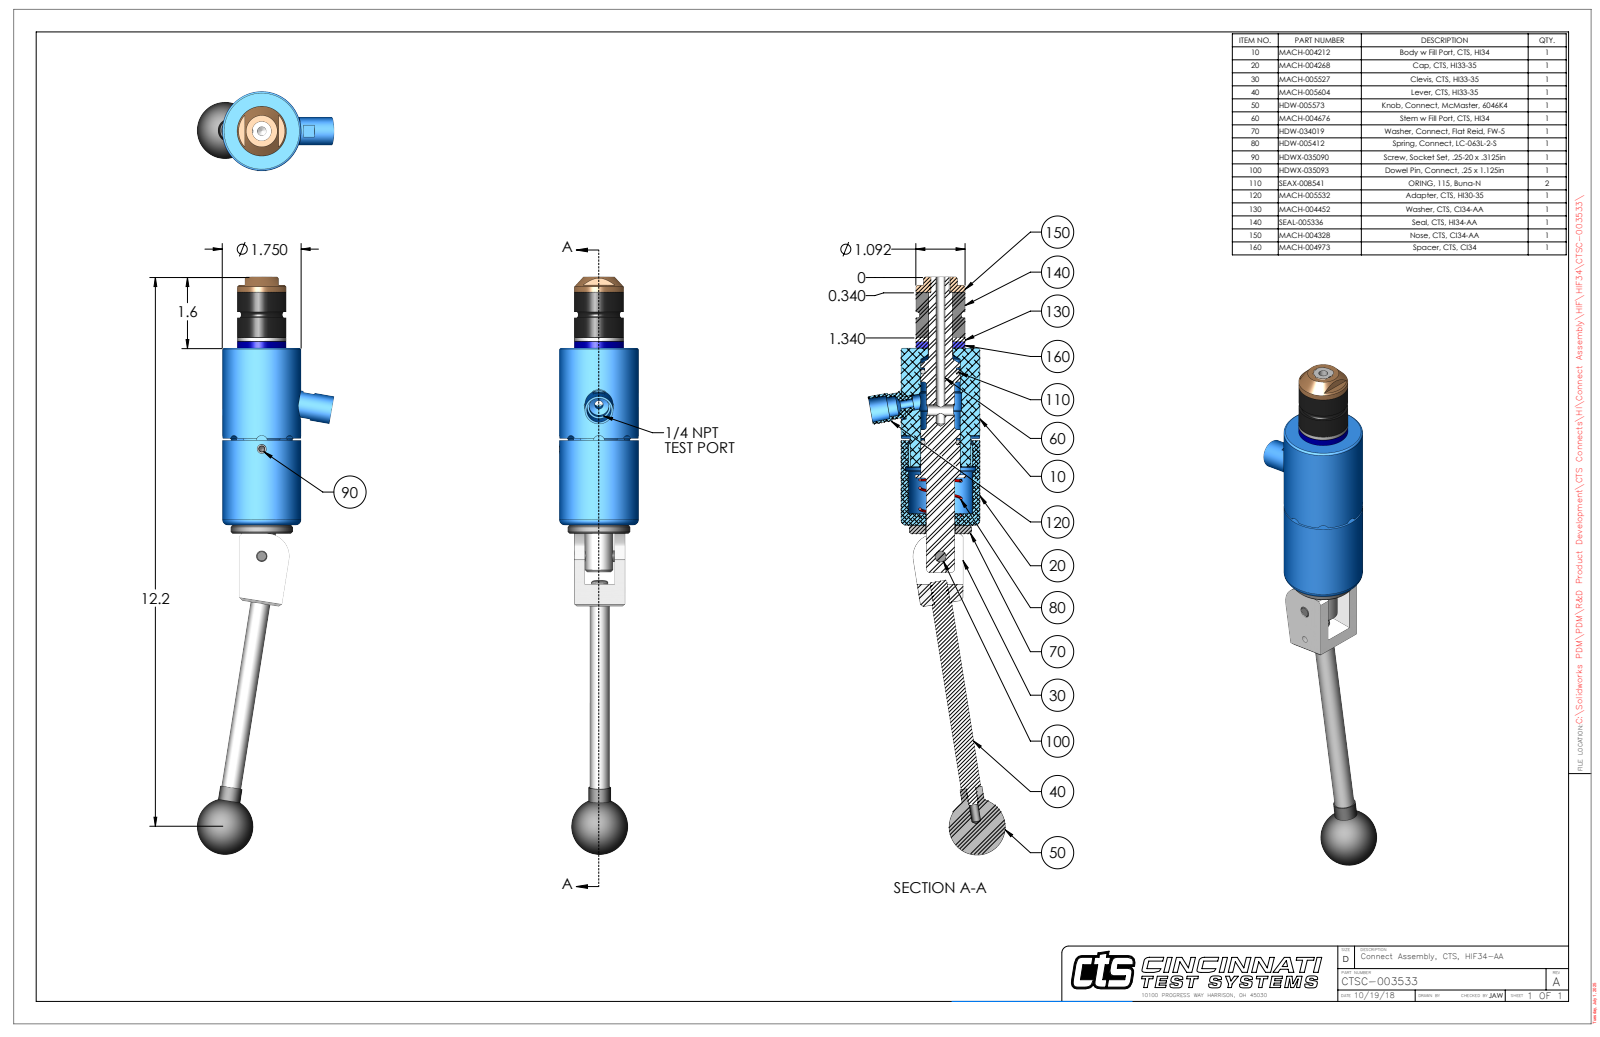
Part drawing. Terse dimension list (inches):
name: CTSC-003533
written by: SolidWorks 2023 (AUTOMOTIVE_DESIGN)
unit: in
bodies: 10 solids, 291 faces (105 planar, 121 cylindrical, 65 other)
size: 12.795 × 3.043 × 1.75
volume: 13.95 in³; area: 79.02 in²
holes: 2× ⌀0.201, 1× ⌀0.15, 1× ⌀0.187, 1× ⌀0.204, 1× ⌀0.249, 1× ⌀0.25, 1× ⌀0.251, 1× ⌀0.313, 1× ⌀0.422, 1× ⌀0.438, 1× ⌀0.53, 1× ⌀0.541
bosses: 2× ⌀0.5, 2× ⌀0.44, 2× ⌀0.25, 1× ⌀1.75, 1× ⌀1.38, 1× ⌀1.092, 1× ⌀1.09, 1× ⌀0.625
rounds: 4× R0.125, 2× R0.029, 1× R0.159, 1× R0.33, 1× R0.5, 1× R0.695, 1× R0.812, 1× R0.842
face distances: 3.921, 1.237, 5.158, 1.12, 1, 0.237, 4.158, 1.094, 0.094, 0.143
hole spacings: 0.74, 2.376, 3.116
